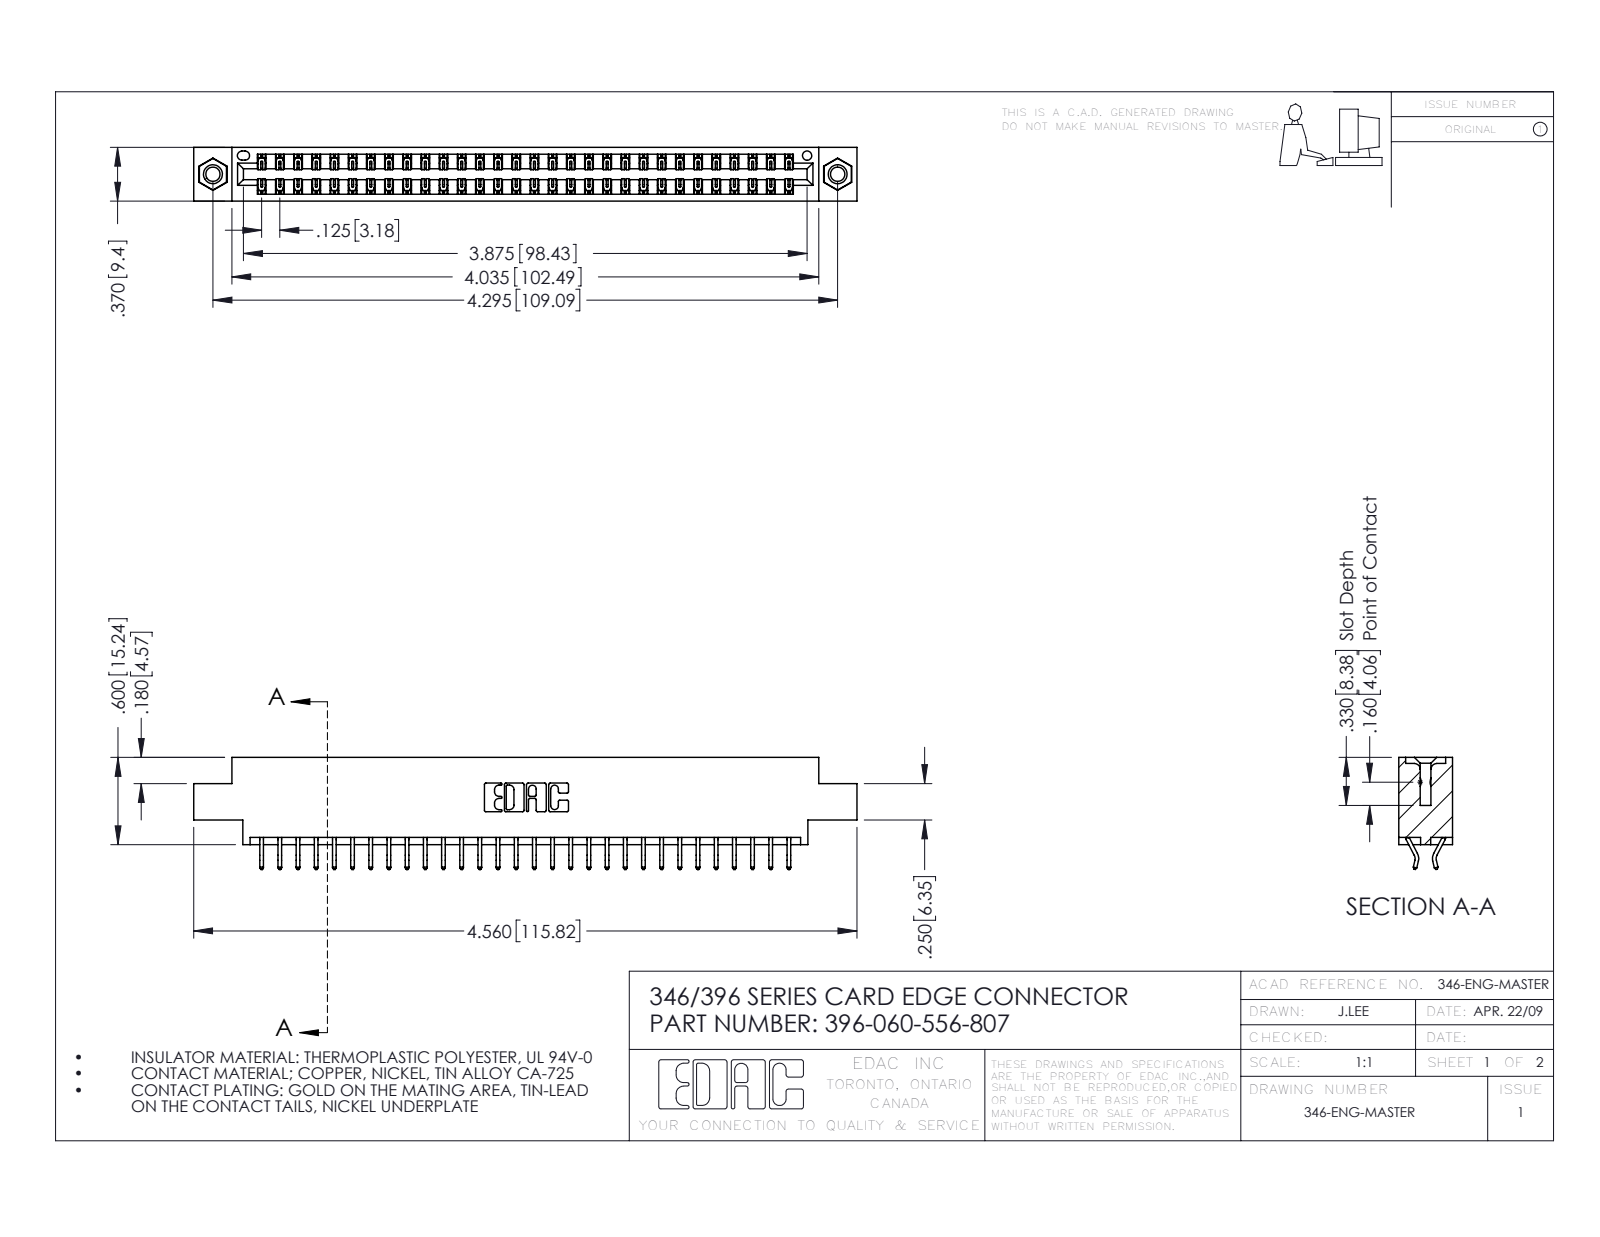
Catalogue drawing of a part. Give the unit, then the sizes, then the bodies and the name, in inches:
Units: inches
Overall size (bounding box): 4.56 × 0.77 × 0.37
Round holes (diameter × count): ⌀0.098 ×2, ⌀0.125 ×2, ⌀0.156 ×2, ⌀0.064 ×1
Round bosses / shafts (diameter × count): ⌀0.155 ×2
Partial cylindrical surfaces — rounded edges, fillets, slot ends (radius × count): R0.006 ×90, R0.01 ×22, R0.007 ×6, R0.031 ×6, R0.026 ×3, R0.01 ×2, R0.014 ×2, R0.022 ×2
Main face-to-face distances: 0.048, 0.322, 0.37, 0.25, 0.025, 0.072, 0.298, 0.275, 0.222, 0.148
Hole centre spacings: 0.246, 4.087, 4.295
Volume: 0.673 in³ · Surface area: 23.45 in²
Bodies: 63 solids, 3666 faces (2452 planar, 1198 cylindrical, 16 other)
Part name (STEP PRODUCT): 345-250-001_345-250-005-103; 345-292-001_556 Tail; 346 Part_0.170 Offset - 0.156 Dia-TI; 396-060-556-807
STEP written by: SolidWorks 2016 (CONFIG_CONTROL_DESIGN)
